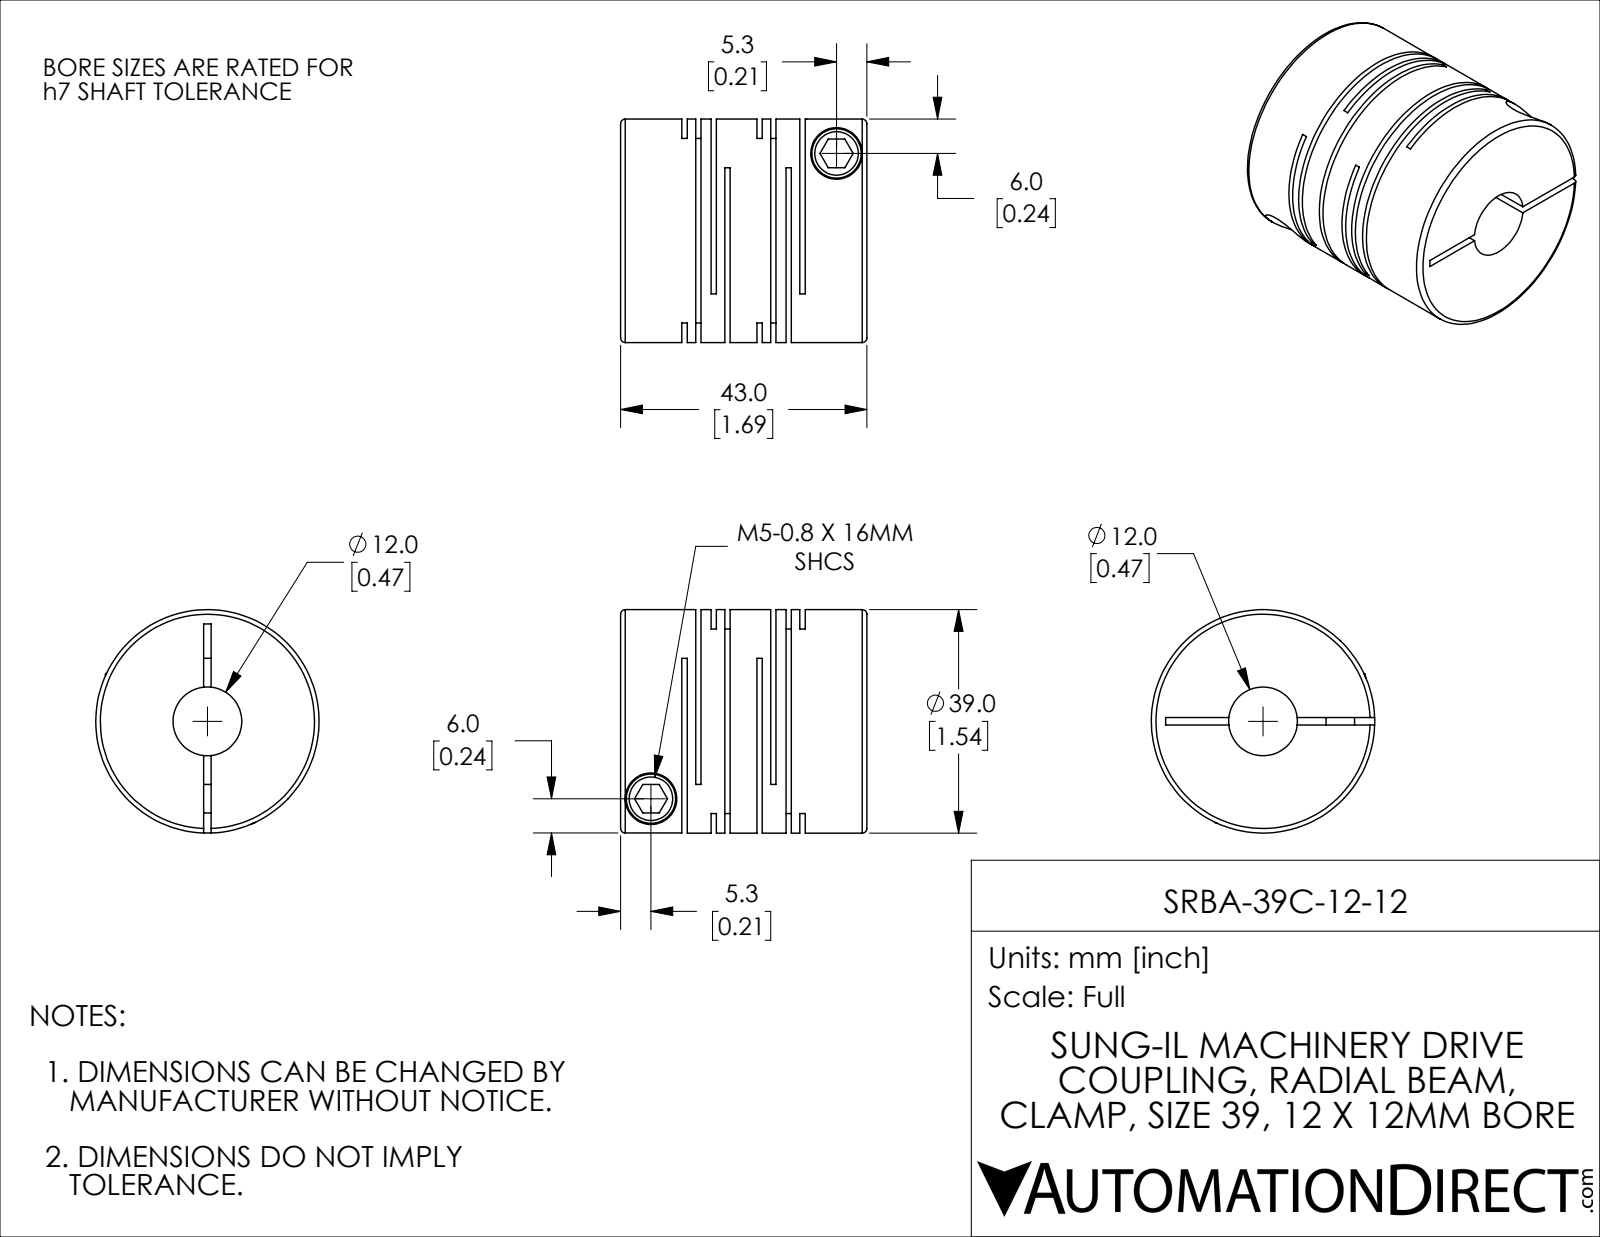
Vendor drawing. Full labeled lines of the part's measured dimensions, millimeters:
Part name (STEP PRODUCT): SRBA-39C-12-12
STEP written by: SolidWorks 2021 (CONFIG_CONTROL_DESIGN)
Units: millimetres
Bodies: 1 solid, 114 faces (60 planar, 42 cylindrical, 12 other)
Overall size (bounding box): 43 × 39 × 39
Volume: 38 367 mm³ · Surface area: 24 241 mm²
Round holes (diameter × count): ⌀5 ×2, ⌀9 ×2, ⌀12 ×1
Round bosses / shafts (diameter × count): ⌀8.6 ×2, ⌀39 ×1
Main face-to-face distances: 13.1, 0.92, 2.4, 5.1, 10.7, 14.02, 18.2, 1.48, 12.18, 4.18
